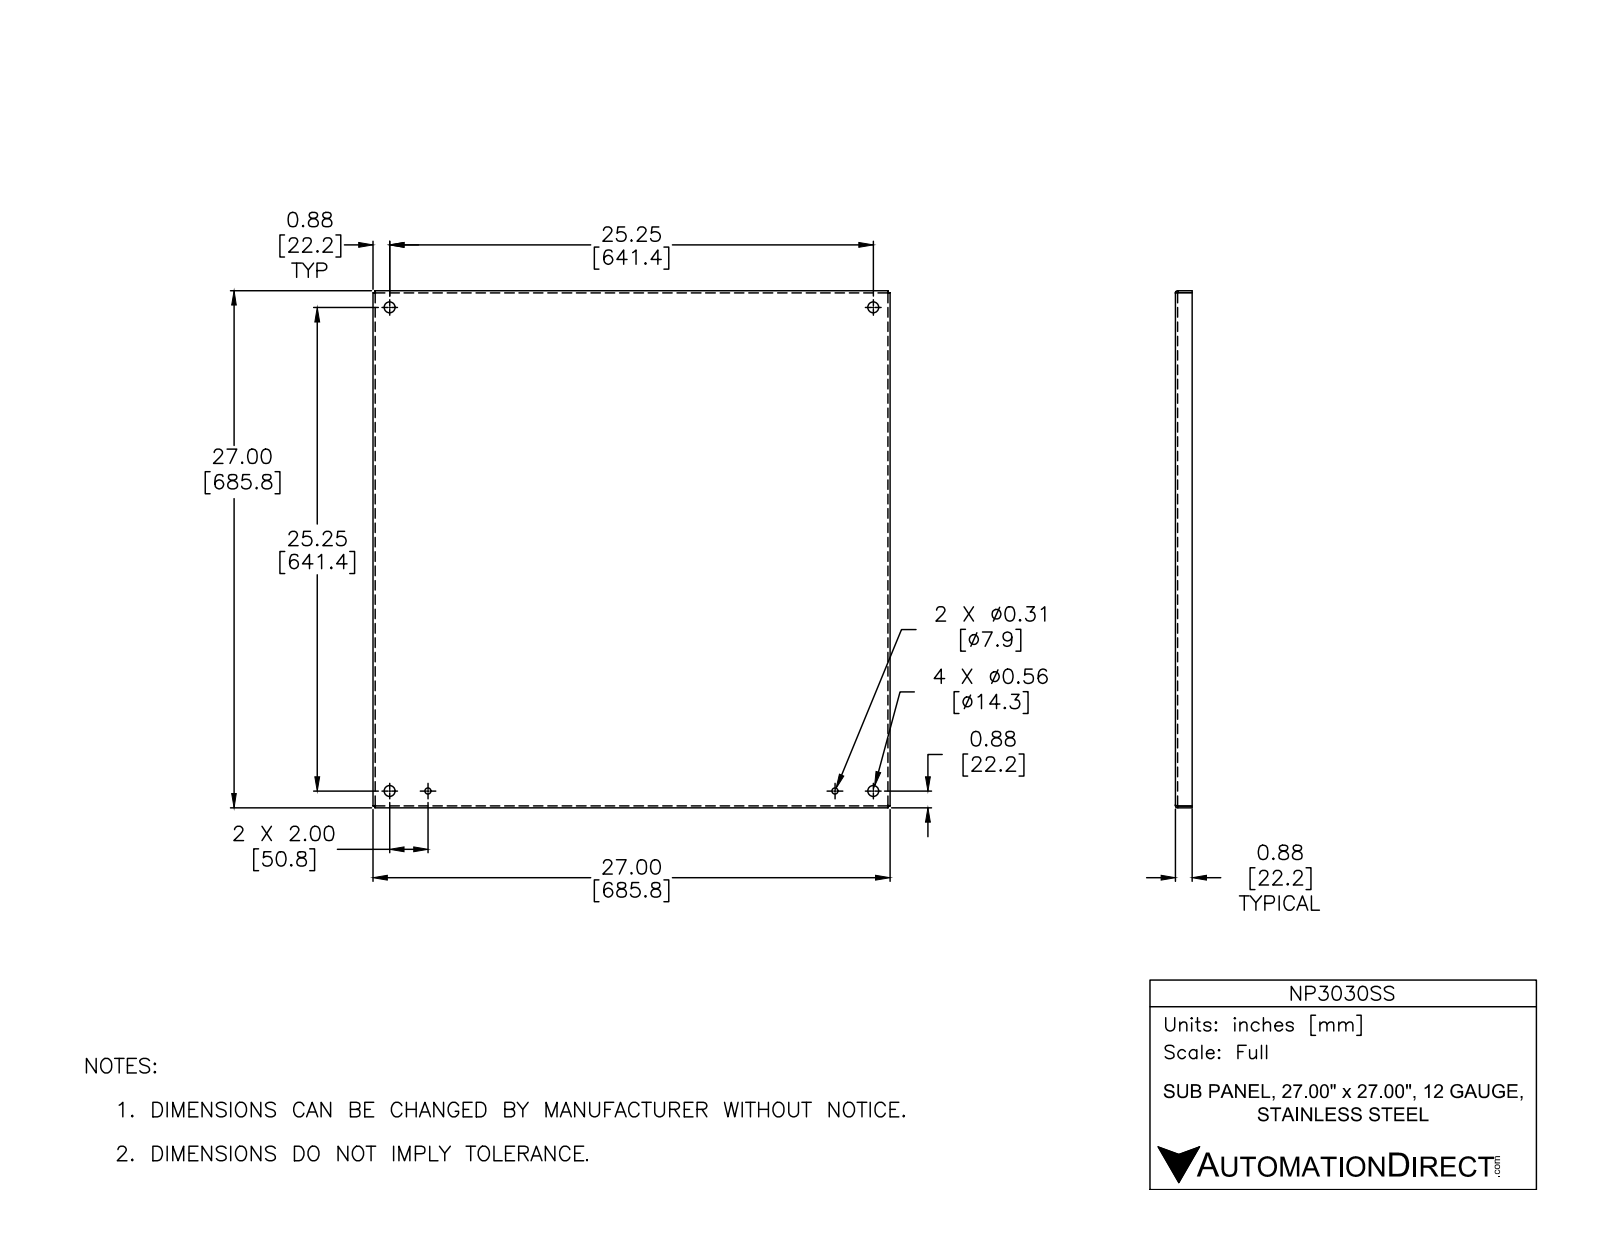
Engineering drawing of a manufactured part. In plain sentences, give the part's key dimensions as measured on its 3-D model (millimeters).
The part is named "NP3030SS". Its 3-D file was written by "Autodesk Inventor 2012 (AUTOMOTIVE_DESIGN)". It is 1 solid with 44 faces: 22 planar, 14 cylindrical and 8 other. Overall it measures 685.8 by 685.8 by 22.2 millimeters. Its volume is 1 241 000 cubic millimeters and its surface area 1 050 000 square millimeters. Round holes: 4 of diameter 14.3, 2 of diameter 7.9. Partial cylindrical surfaces (rounded edges, fillets, slot ends): 4 of radius 0.8, 4 of radius 3.2. The main face-to-face distances are 2.4, 683.4, 685.8, 681.1, 19.8, 22.2, 2.7, 683.1, 680.8, 680.5. The hole center spacings are 641.4, 643.4, 907, 50.8, 50.8, 539.8, 590.6, 590.6.
